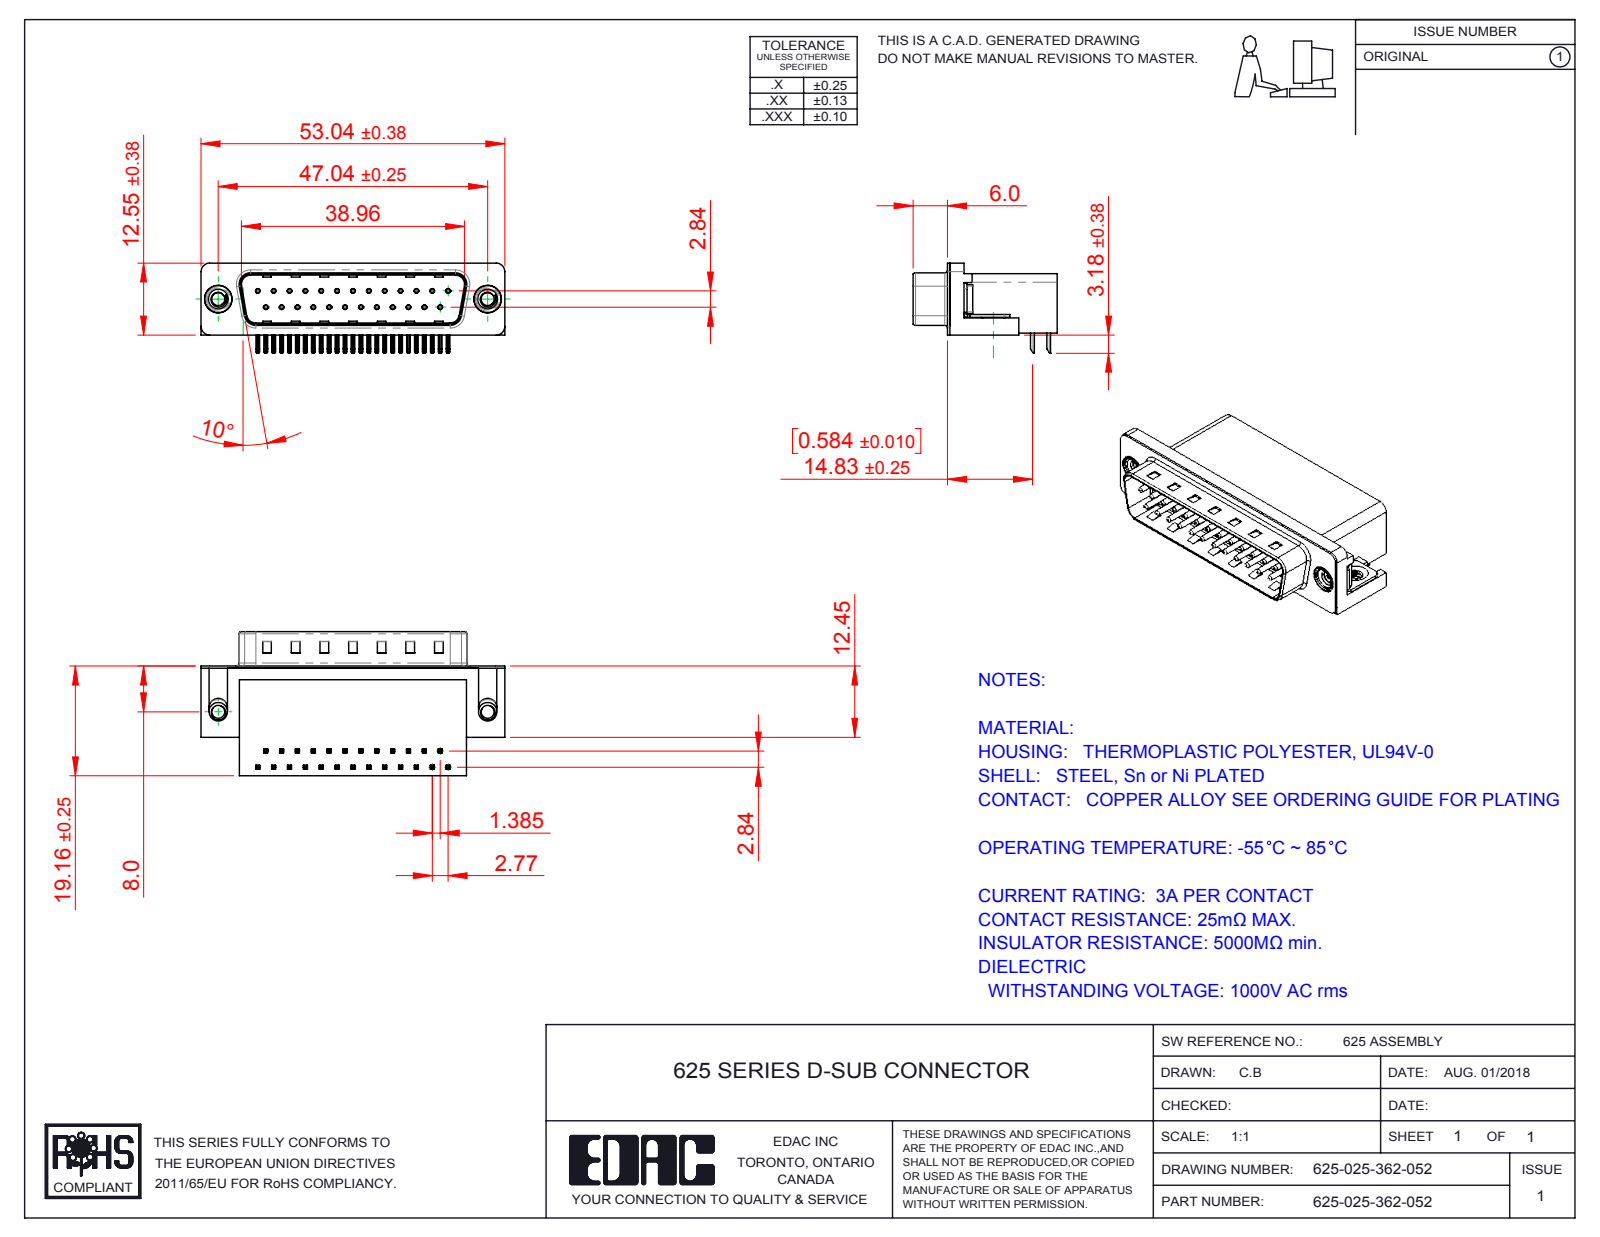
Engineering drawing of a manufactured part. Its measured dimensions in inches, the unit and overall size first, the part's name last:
Units: inches
Overall size (bounding box): 2.088 × 0.991 × 0.619
Round holes (diameter × count): ⌀0.014 ×25, ⌀0.031 ×25, ⌀0.089 ×4, ⌀0.157 ×2, ⌀0.189 ×2, ⌀0.197 ×2
Round bosses / shafts (diameter × count): ⌀0.03 ×25, ⌀0.193 ×2, ⌀0.187 ×2, ⌀0.154 ×2, ⌀0.128 ×2
Partial cylindrical surfaces — rounded edges, fillets, slot ends (radius × count): R0.01 ×108, R0.005 ×50, R0.039 ×16, R0.02 ×9, R0.063 ×8, R0.059 ×7, R0.035 ×4, R0.079 ×4
Main face-to-face distances: 0.016, 0.407, 0.739, 0.083, 0.345, 0.412, 0.428, 0.067, 0.754, 0.398
Hole centre spacings: 0.124, 0.109, 0.436, 0.218, 0.327, 0.198, 0.545, 0.294
Volume: 0.56 in³ · Surface area: 13.86 in²
Bodies: 31 solids, 2297 faces (1407 planar, 673 cylindrical, 217 other)
Part name (STEP PRODUCT): 625 4-40 Threaded Board Mount; 625 4-40 Threaded Rivet; 625 Contact Bottom; 625-025-362-052 (+3 more)
STEP written by: SolidWorks 2016 (CONFIG_CONTROL_DESIGN)
